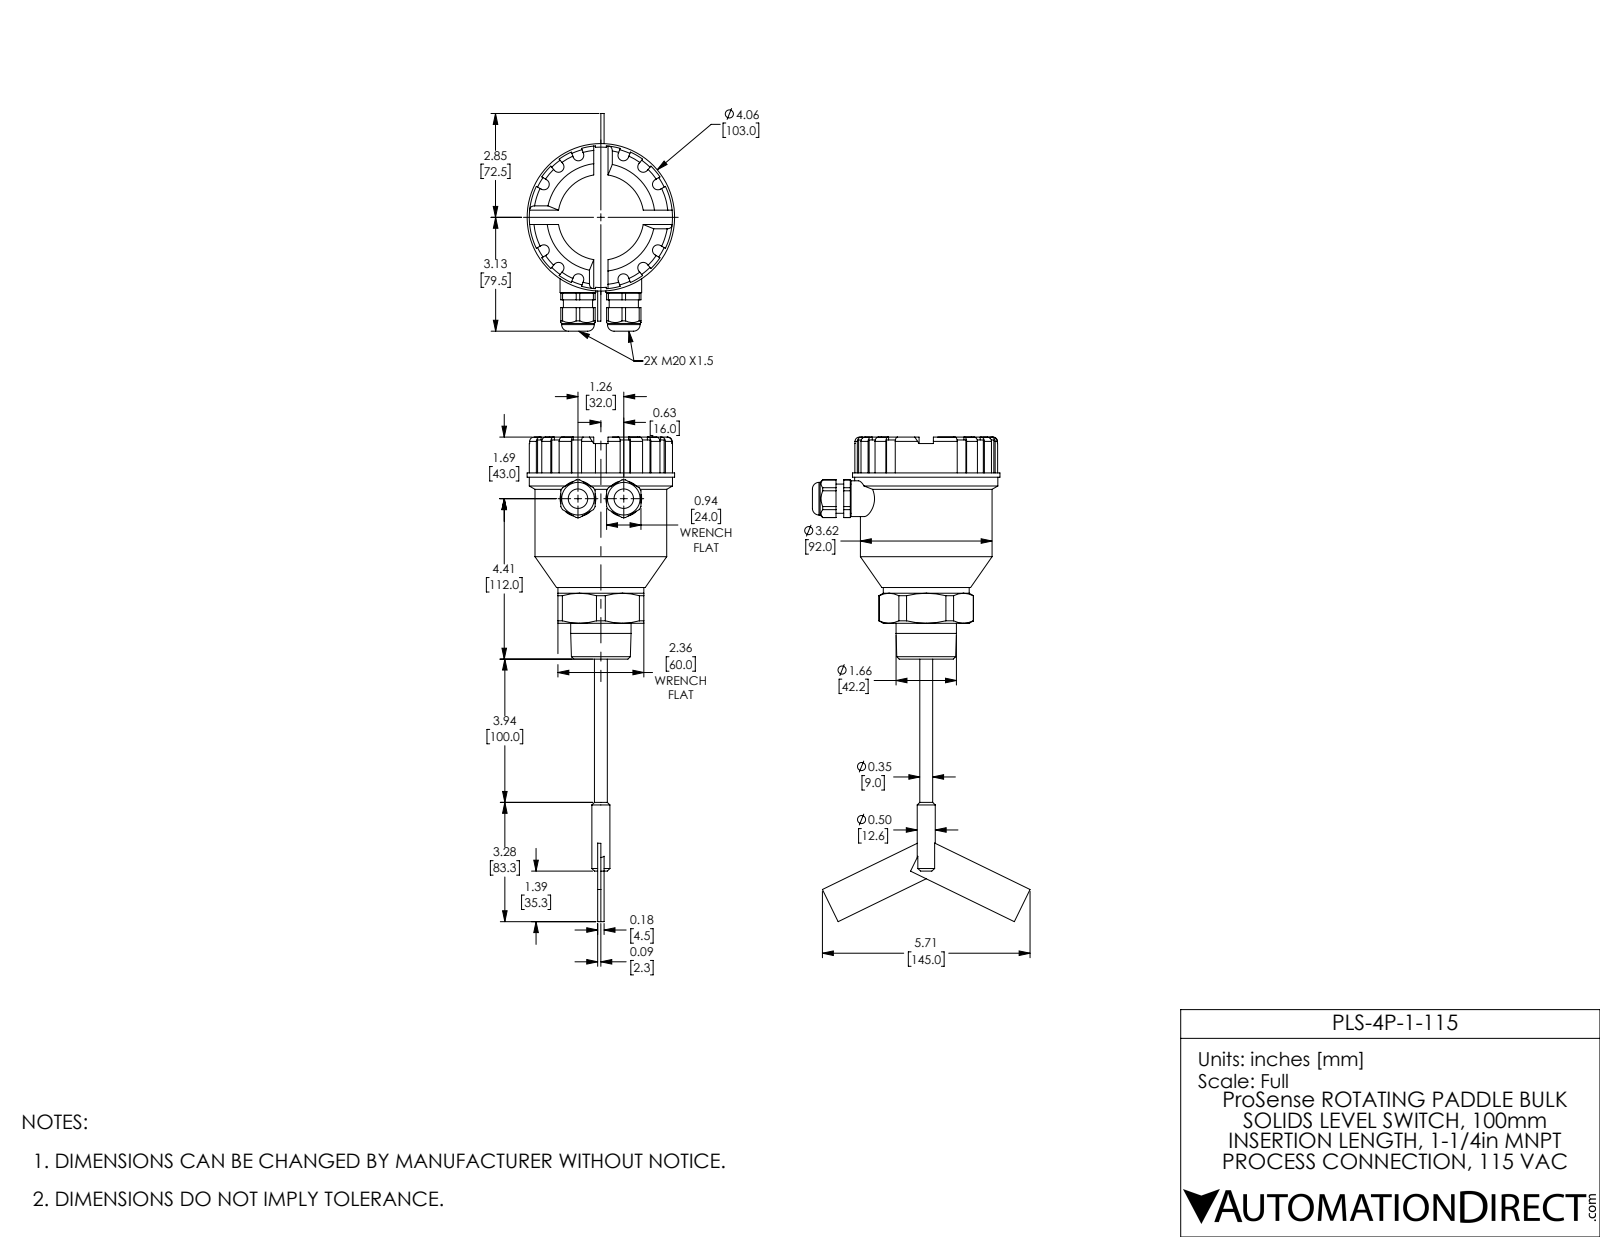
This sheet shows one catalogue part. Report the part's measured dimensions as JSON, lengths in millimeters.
{"part_name": "100mm Shaft", "step_written_by": "SolidWorks 2017 (AUTOMOTIVE_DESIGN)", "units": "millimeters", "bodies": {"solids": 1, "faces": 279, "planar": 112, "cylindrical": 112, "other": 55}, "overall_size": [338.3, 152, 103], "volume_mm3": 839200, "surface_area_mm2": 72000, "round_bosses_or_shafts": [[25, 2], [22.8, 2], [20.4, 2], [103, 1], [100, 1], [92, 1], [60, 1], [42.2, 1]], "partial_cylinders_radius": [[3.8, 12], [13.2, 2], [33, 1], [49, 1]], "face_to_face_distances": [2.3, 4.5, 130, 25, 60, 125.5, 27.8, 30, 32.3, 150.5]}
